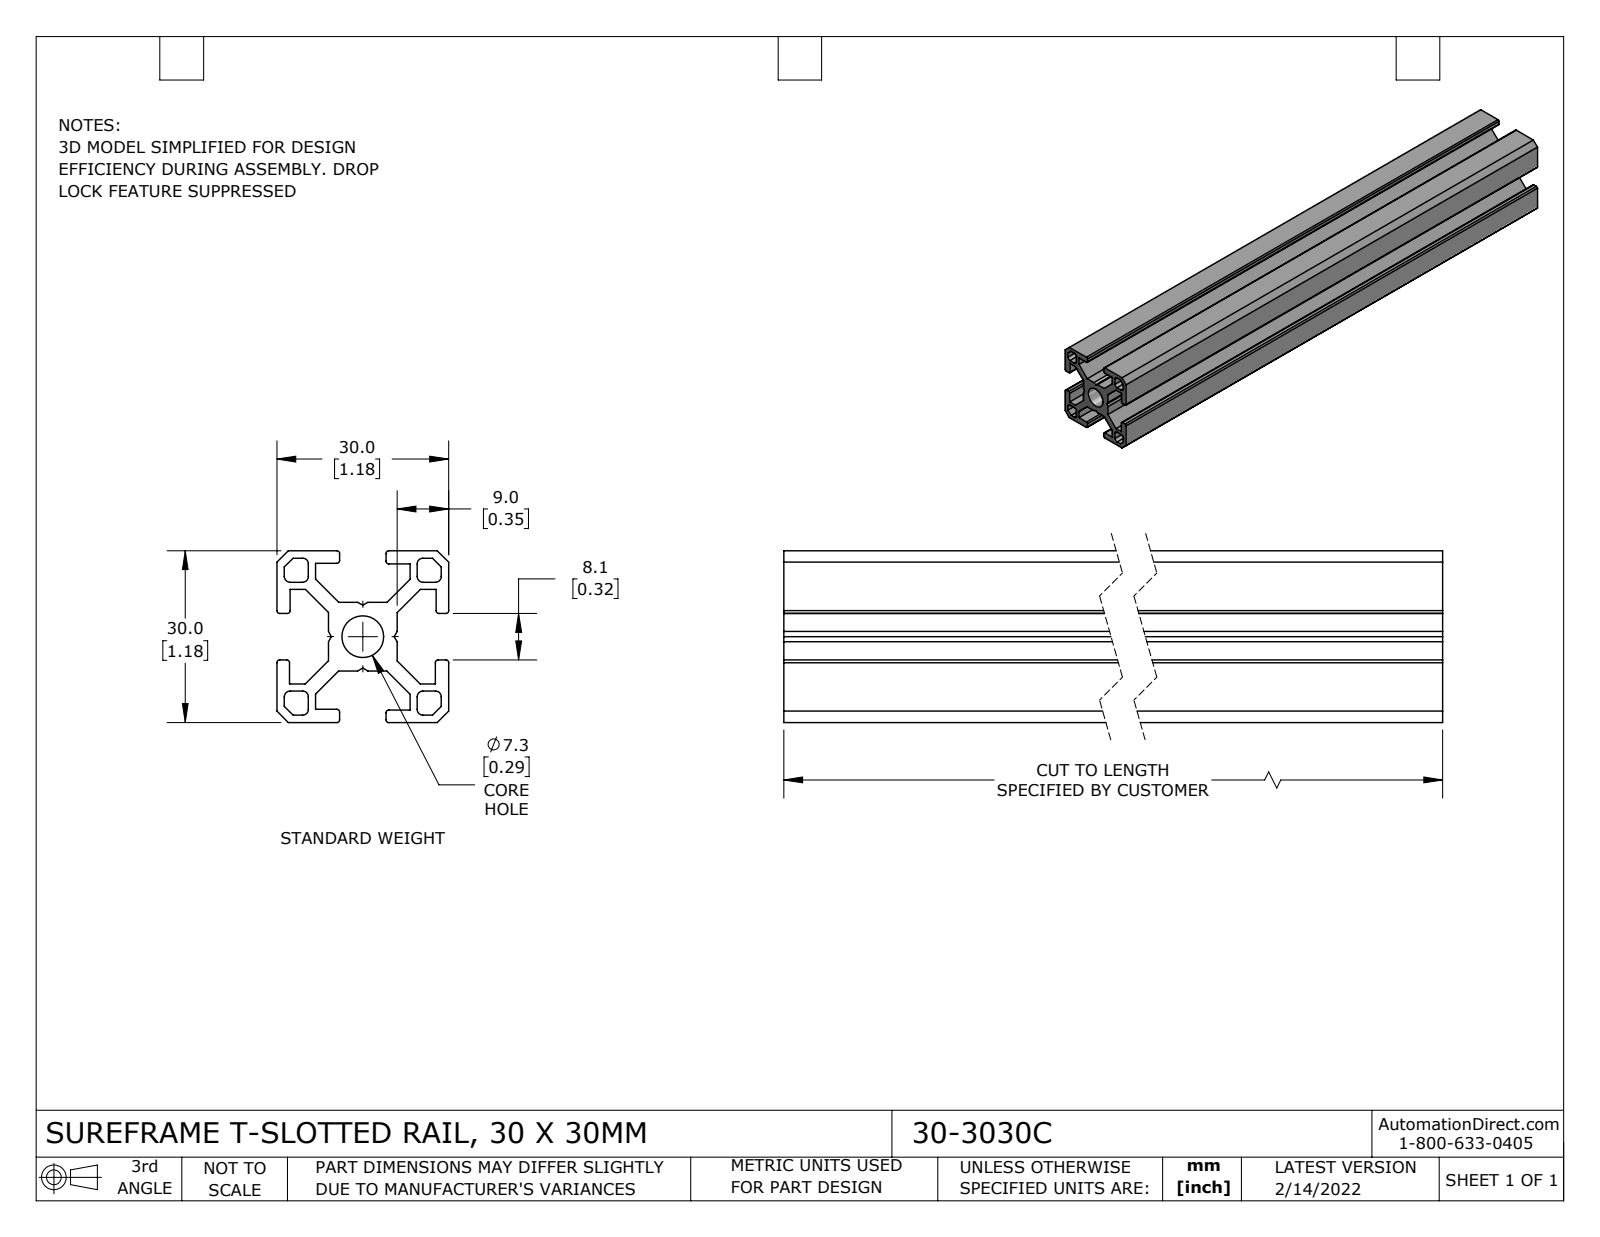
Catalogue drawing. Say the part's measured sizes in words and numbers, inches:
The part is named "30-3030C". Its 3-D file was written by "SolidWorks 2021 (CONFIG_CONTROL_DESIGN)". It is 1 solid with 112 faces: 82 planar, 30 cylindrical and 0 other. Overall it measures 8 by 1.181 by 1.181 inches. Its volume is 4.105 cubic inches and its surface area 100.1 square inches. Round holes: 1 of diameter 0.287. Partial cylindrical surfaces (rounded edges, fillets, slot ends): 16 of radius 0.02, 12 of radius 0.039. The main face-to-face distances are 1.181, 0.699, 0.354, 0.827, 0.829, 0.165, 0.215, 0.099, 0.266, 0.915.
